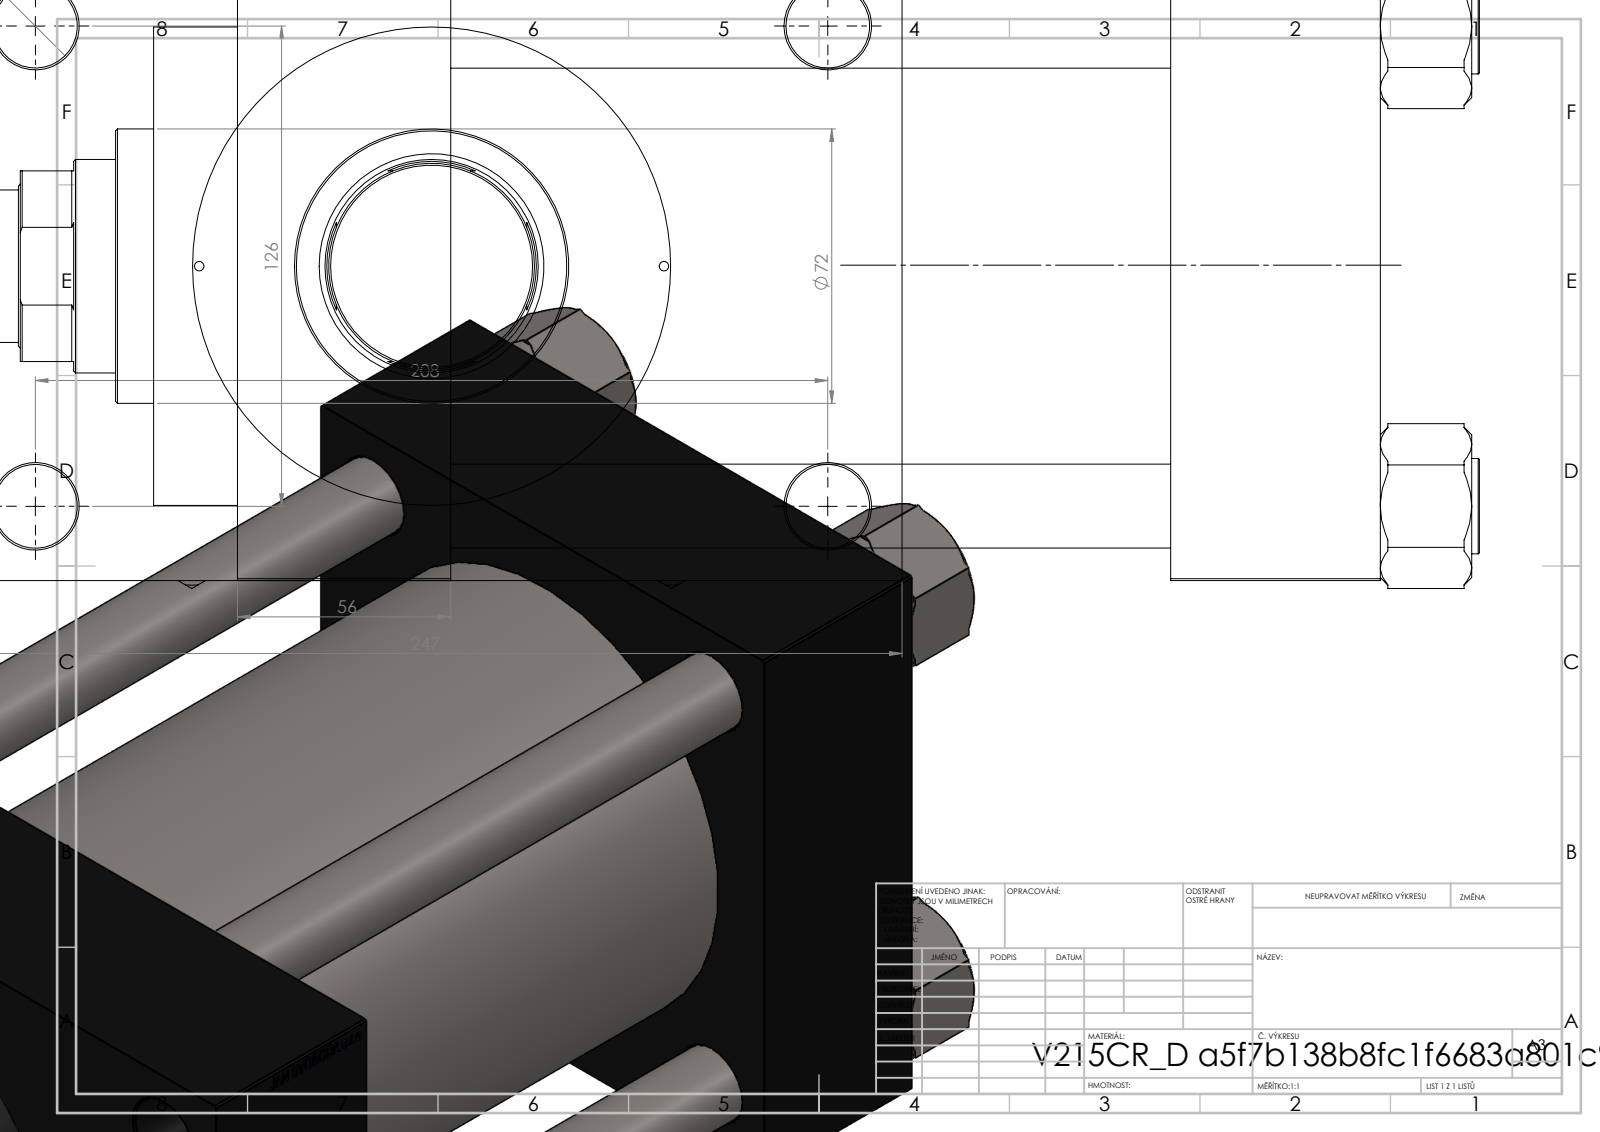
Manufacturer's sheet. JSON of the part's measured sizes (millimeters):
{"part_name": "V215_VC_A; V215CR_ROD_END_F; V215CR_VCP_D; NUT_M5_D (+2 more)", "step_written_by": "SolidWorks 2019 (CONFIG_CONTROL_DESIGN)", "units": "millimeters", "bodies": {"solids": 12, "faces": 1168, "planar": 550, "cylindrical": 94, "other": 524}, "overall_size": [435, 247, 169.14], "volume_mm3": 5562000, "surface_area_mm2": 678624, "round_holes": [[22, 8], [2.5, 2], [7, 2], [32.24, 2], [45, 2], [40.5, 1], [56, 1], [59, 1], [96, 1], [125, 1], [125.5, 1]], "round_bosses_or_shafts": [[25, 4], [131, 1], [72, 1], [54, 1], [40, 1]], "face_to_face_distances": [165, 189, 244, 55, 245, 56, 300, 41, 206, 278.74], "hole_center_spacings": [41.05, 62.98, 76.28, 89.02, 121.59, 125.9, 132.47, 139.02]}
